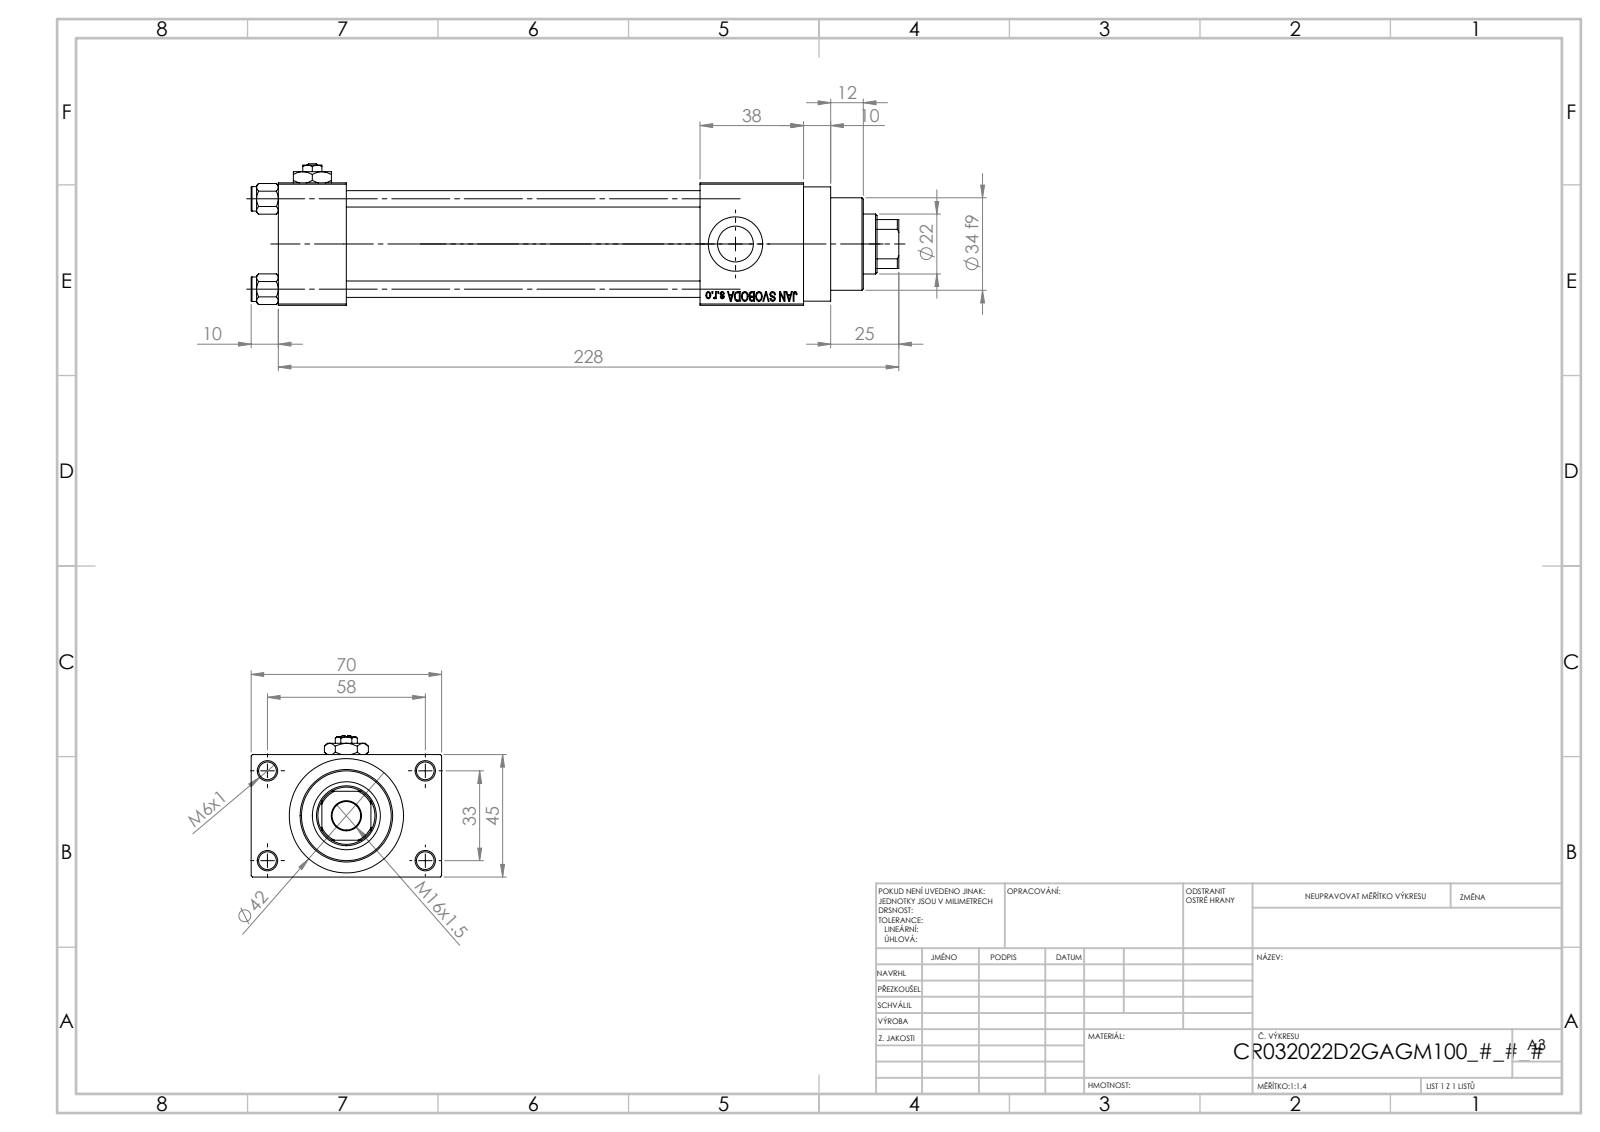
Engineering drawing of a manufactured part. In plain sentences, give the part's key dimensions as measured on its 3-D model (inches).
The part is named "V215CR_D_TYCINKA; Zatka_pro_OIL_PORT; V215CR_VCP_D; V215_VC_A (+2 more)". Its 3-D file was written by "SolidWorks 2019 (CONFIG_CONTROL_DESIGN)". It is 12 solids with 1145 faces: 518 planar, 89 cylindrical and 538 other. Overall it measures 9.37 by 2.756 by 2.047 inches. Its volume is 18.89 cubic inches and its surface area 170.1 square inches. Round holes: 4 of diameter 0.236, 4 of diameter 0.256, 2 of diameter 0.276, 2 of diameter 0.518, 2 of diameter 0.787, 1 of diameter 0.413, 1 of diameter 0.866, 1 of diameter 0.945, 1 of diameter 0.984, 1 of diameter 1.26, 1 of diameter 1.299. Round bosses or shafts: 4 of diameter 0.354, 1 of diameter 1.654, 1 of diameter 1.496, 1 of diameter 1.339. Partial cylindrical surfaces (rounded edges, fillets, slot ends): 1 of radius 0.413. The main face-to-face distances are 1.772, 0.984, 0.492, 2.264, 5.118, 6.102, 6.614, 1.496, 7.598, 2.756. The hole center spacings are 0.488, 0.924, 1.307, 1.314, 1.392, 1.795, 2.219, 1.299.
